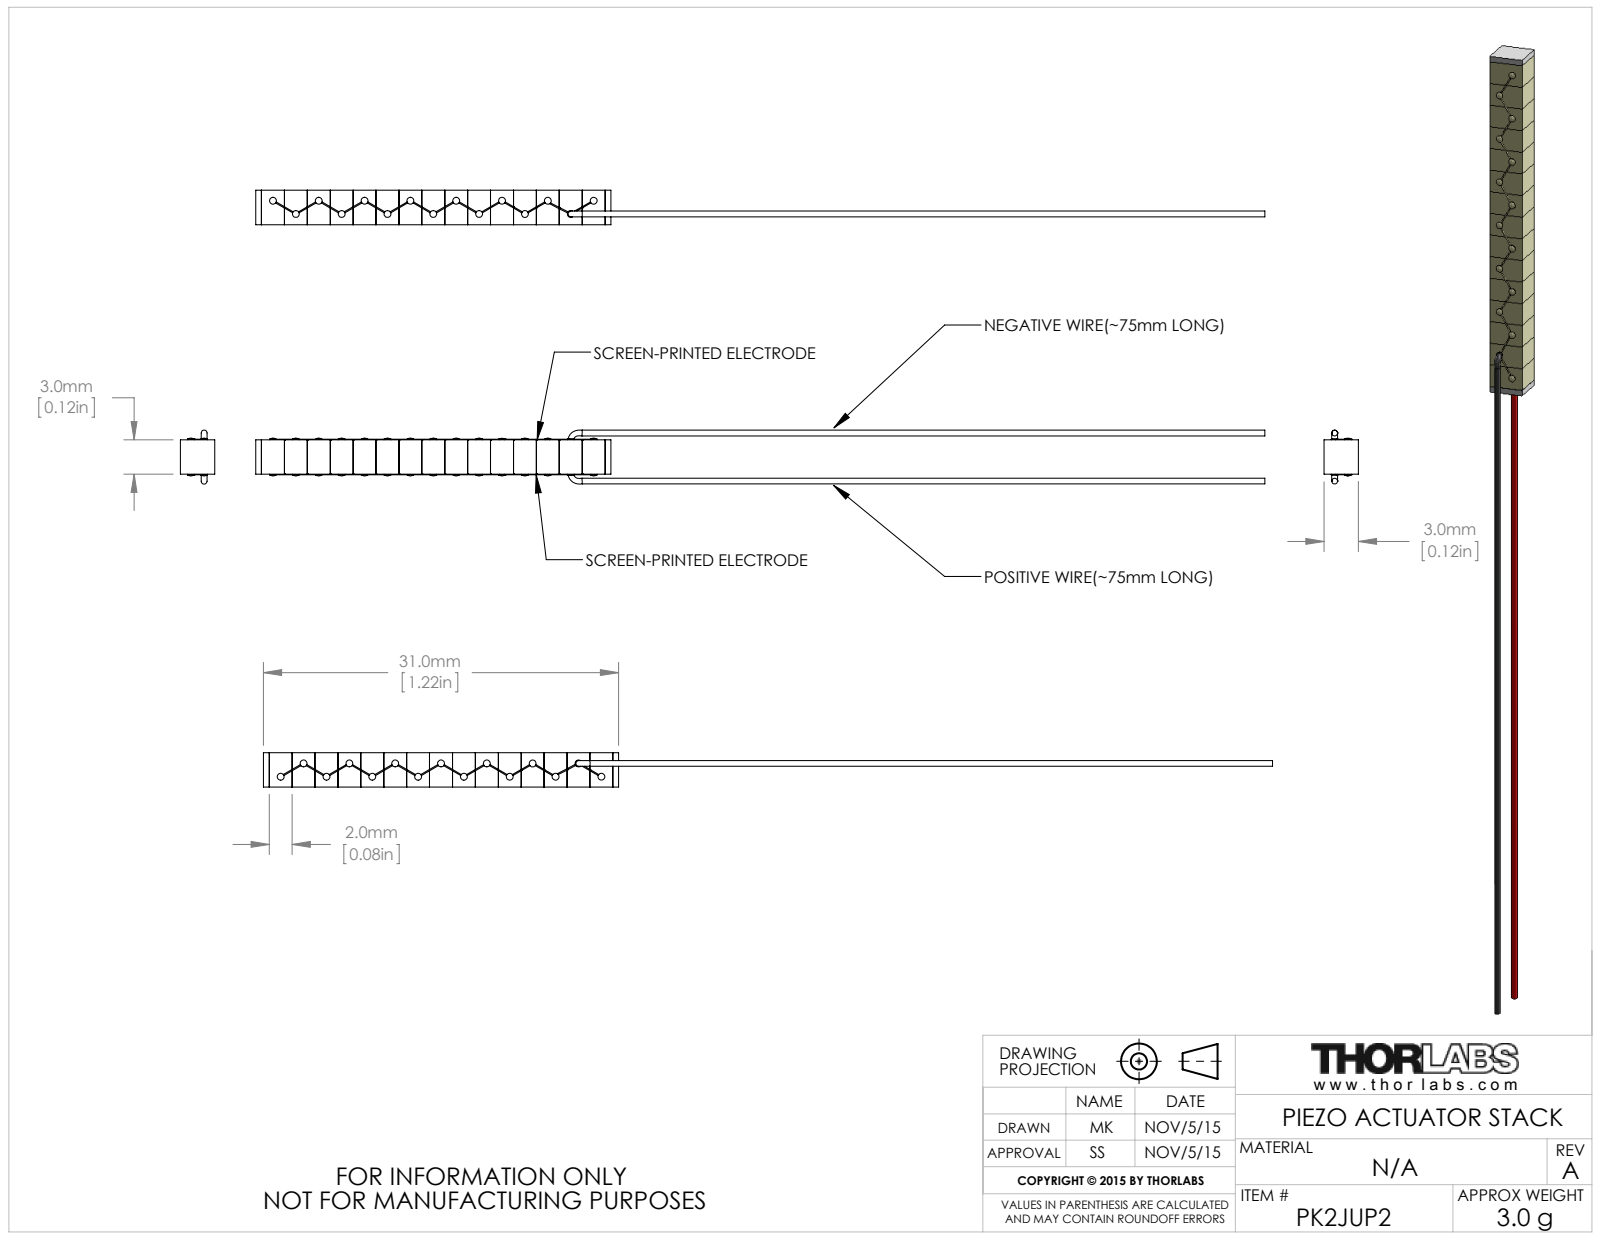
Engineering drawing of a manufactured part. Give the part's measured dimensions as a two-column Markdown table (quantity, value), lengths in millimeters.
| quantity | value |
| --- | --- |
| part name | CTN003189 |
| STEP written by | SolidWorks 2014 (AUTOMOTIVE_DESIGN) |
| units | millimeters |
| bodies | 20 solids, 313 faces (121 planar, 126 cylindrical, 66 other) |
| overall size | 88.1 × 4.72 × 3 |
| volume | 304 mm³ |
| surface area | 893 mm² |
| round bosses / shafts (diameter × count) | 0.6 × 15 |
| main face-to-face distances | 2, 4, 6, 8, 10, 3, 12, 14, 16, 18 |
